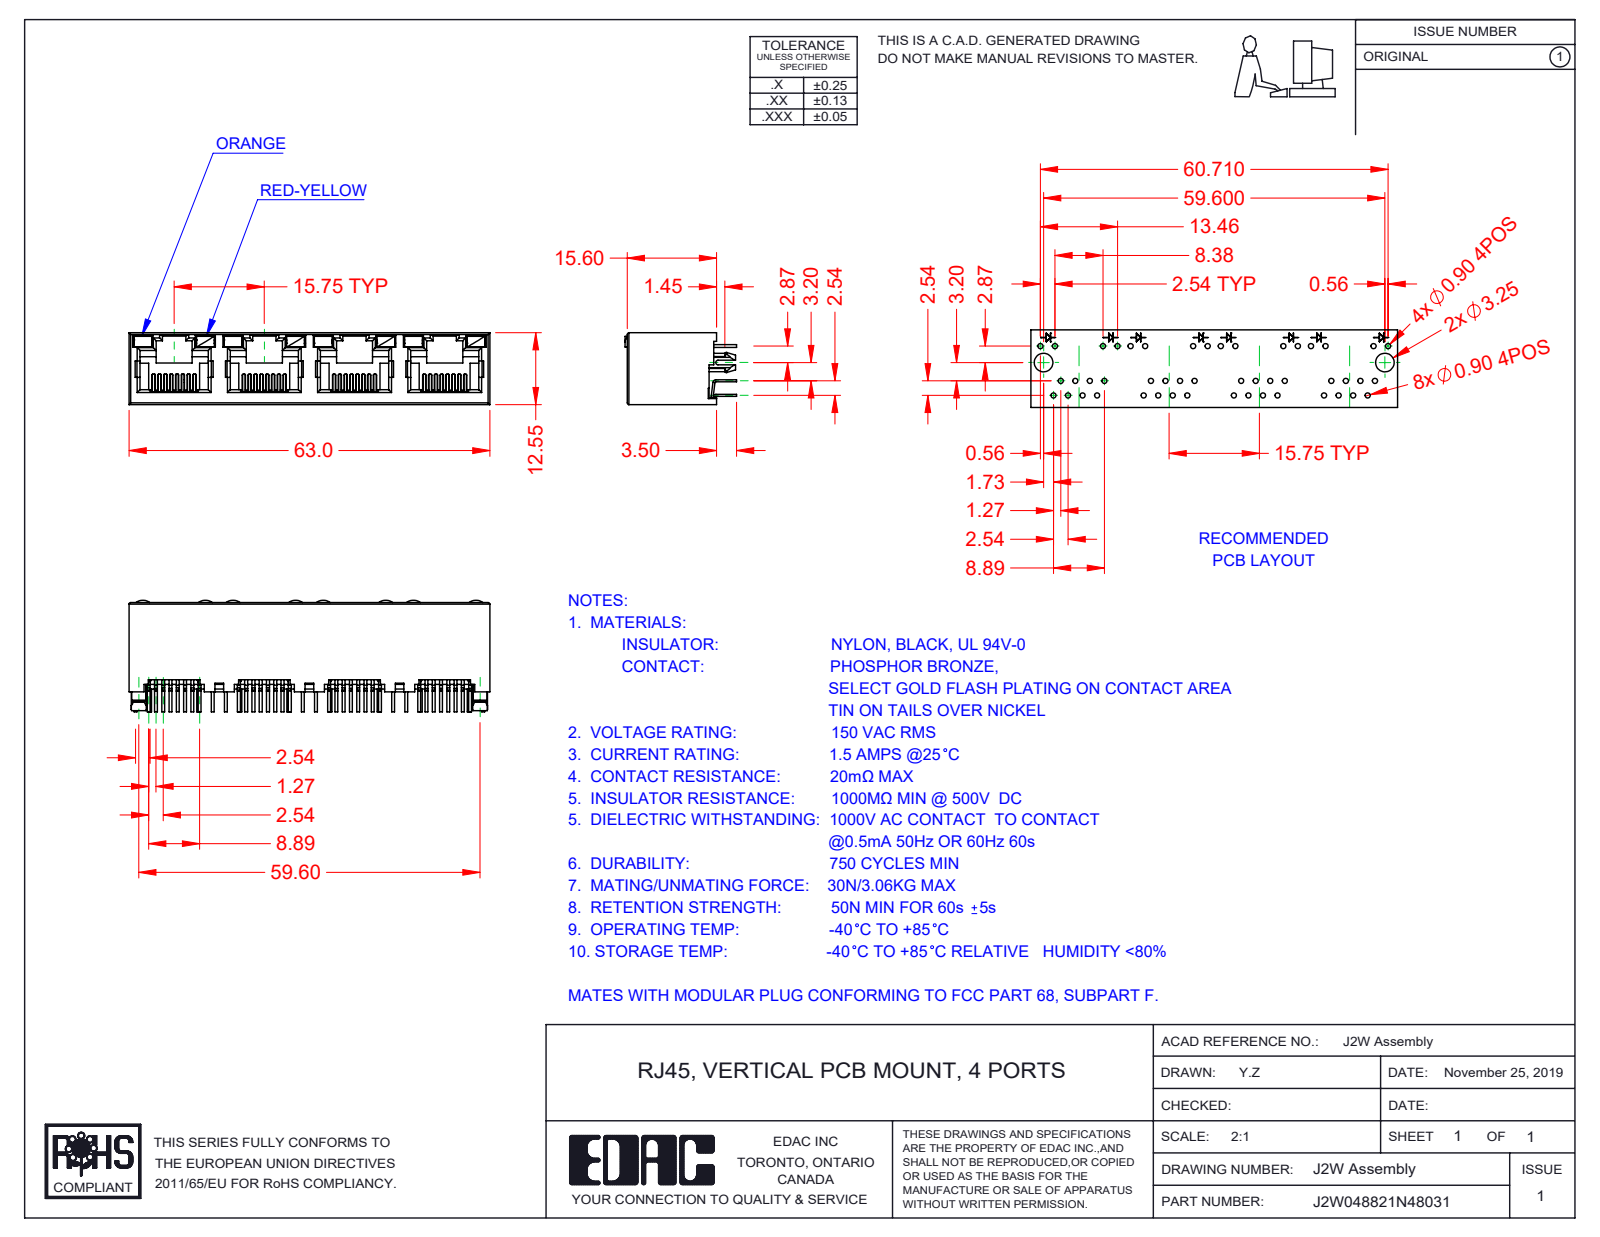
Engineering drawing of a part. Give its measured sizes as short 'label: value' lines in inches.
name: J2W048821N48031; 2W Contact Lock; 2W Insulator; 2W LED LH_4-Orange (+2 more)
written by: SolidWorks 2020 (CONFIG_CONTROL_DESIGN)
unit: in
bodies: 45 solids, 3139 faces (2600 planar, 481 cylindrical, 58 other)
size: 2.48 × 0.768 × 0.494
volume: 0.326 in³; area: 20.37 in²
rounds: 64× R0.006, 29× R0.008, 28× R0.02, 14× R0.012, 8× R0.018, 8× R0.079, 2× R0.01, 2× R0.059
face distances: 0.494, 0.469, 0.026, 0.62, 0.014, 0.059, 0.031, 0.024, 0.445, 1.24
